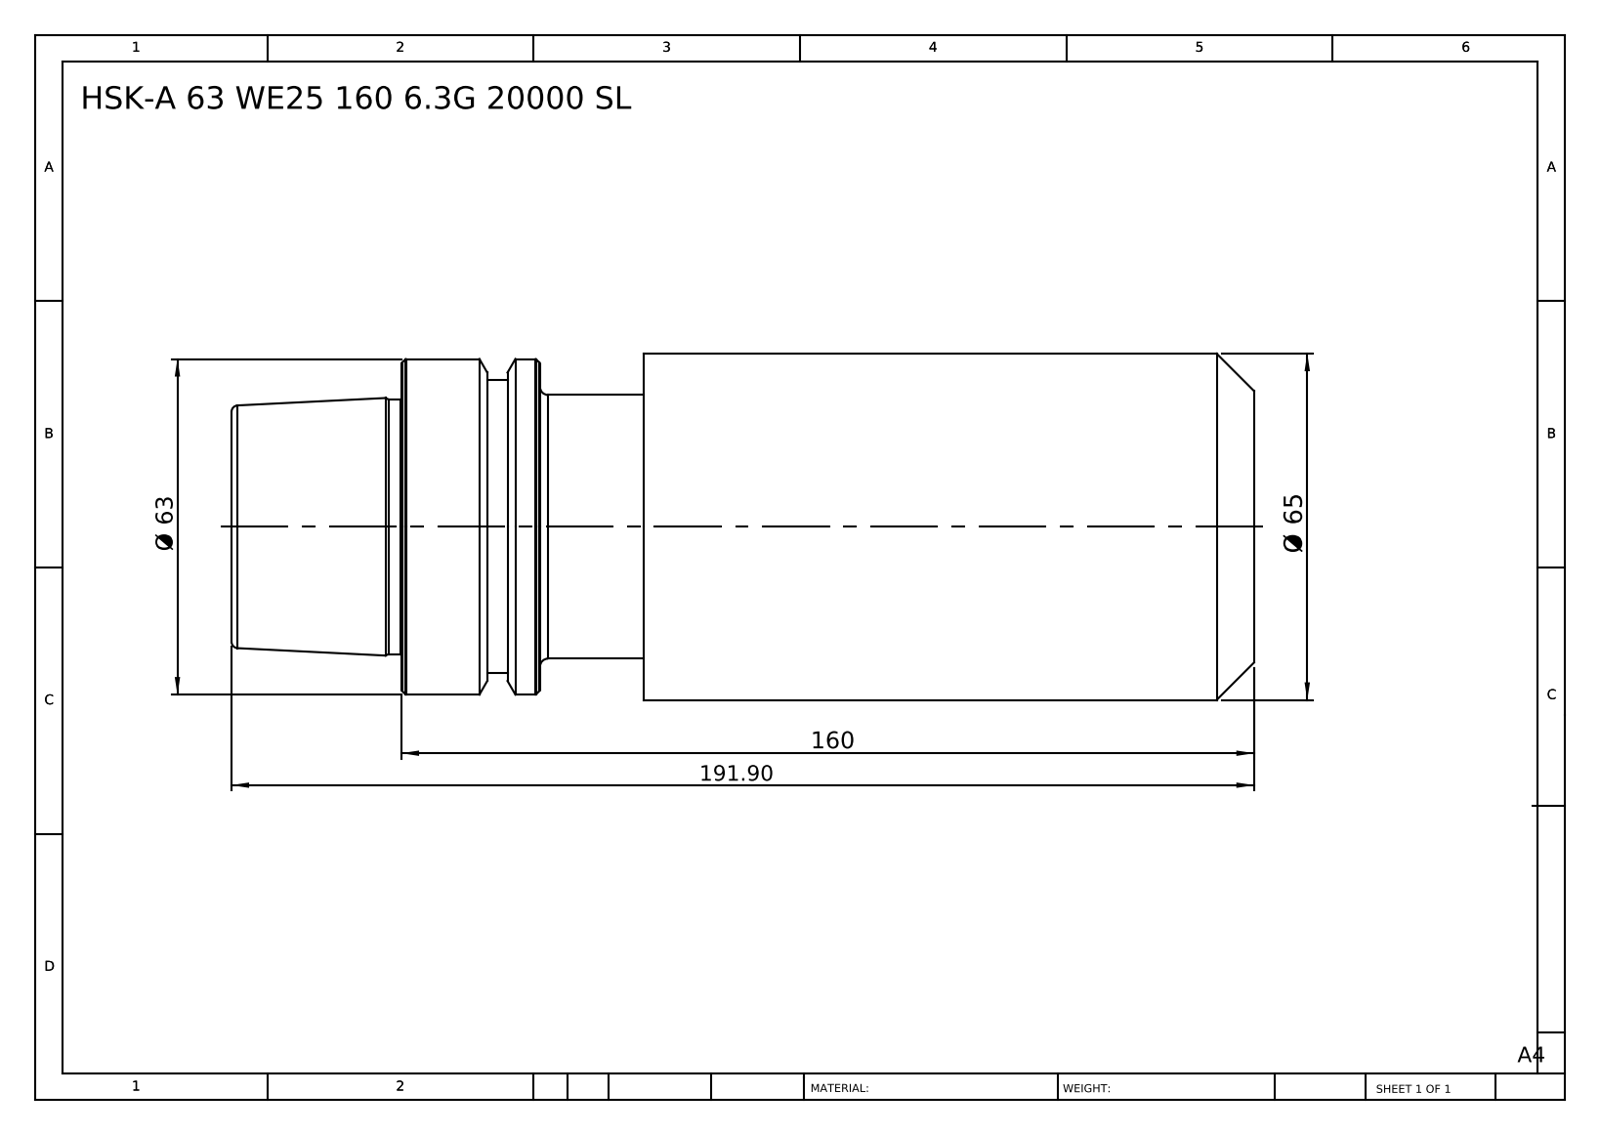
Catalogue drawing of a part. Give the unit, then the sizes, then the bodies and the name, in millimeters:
Units: millimetres
Overall size (bounding box): 191.9 × 65 × 65
Round bosses / shafts (diameter × count): ⌀65 ×1, ⌀63 ×1, ⌀55 ×1, ⌀49.5 ×1, ⌀47.78 ×1
Main face-to-face distances: 191.9, 114.5, 77.4, 134, 19.5, 57.9, 160, 45.5, 26, 31.9
Volume: 545 476 mm³ · Surface area: 44 848 mm²
Bodies: 1 solid, 49 faces (7 planar, 12 cylindrical, 30 other)
Part name (STEP PRODUCT): HSK-A 63 WE25 160 6.3G 20000 SL
STEP written by: SolidWorks 2014 (CONFIG_CONTROL_DESIGN)
